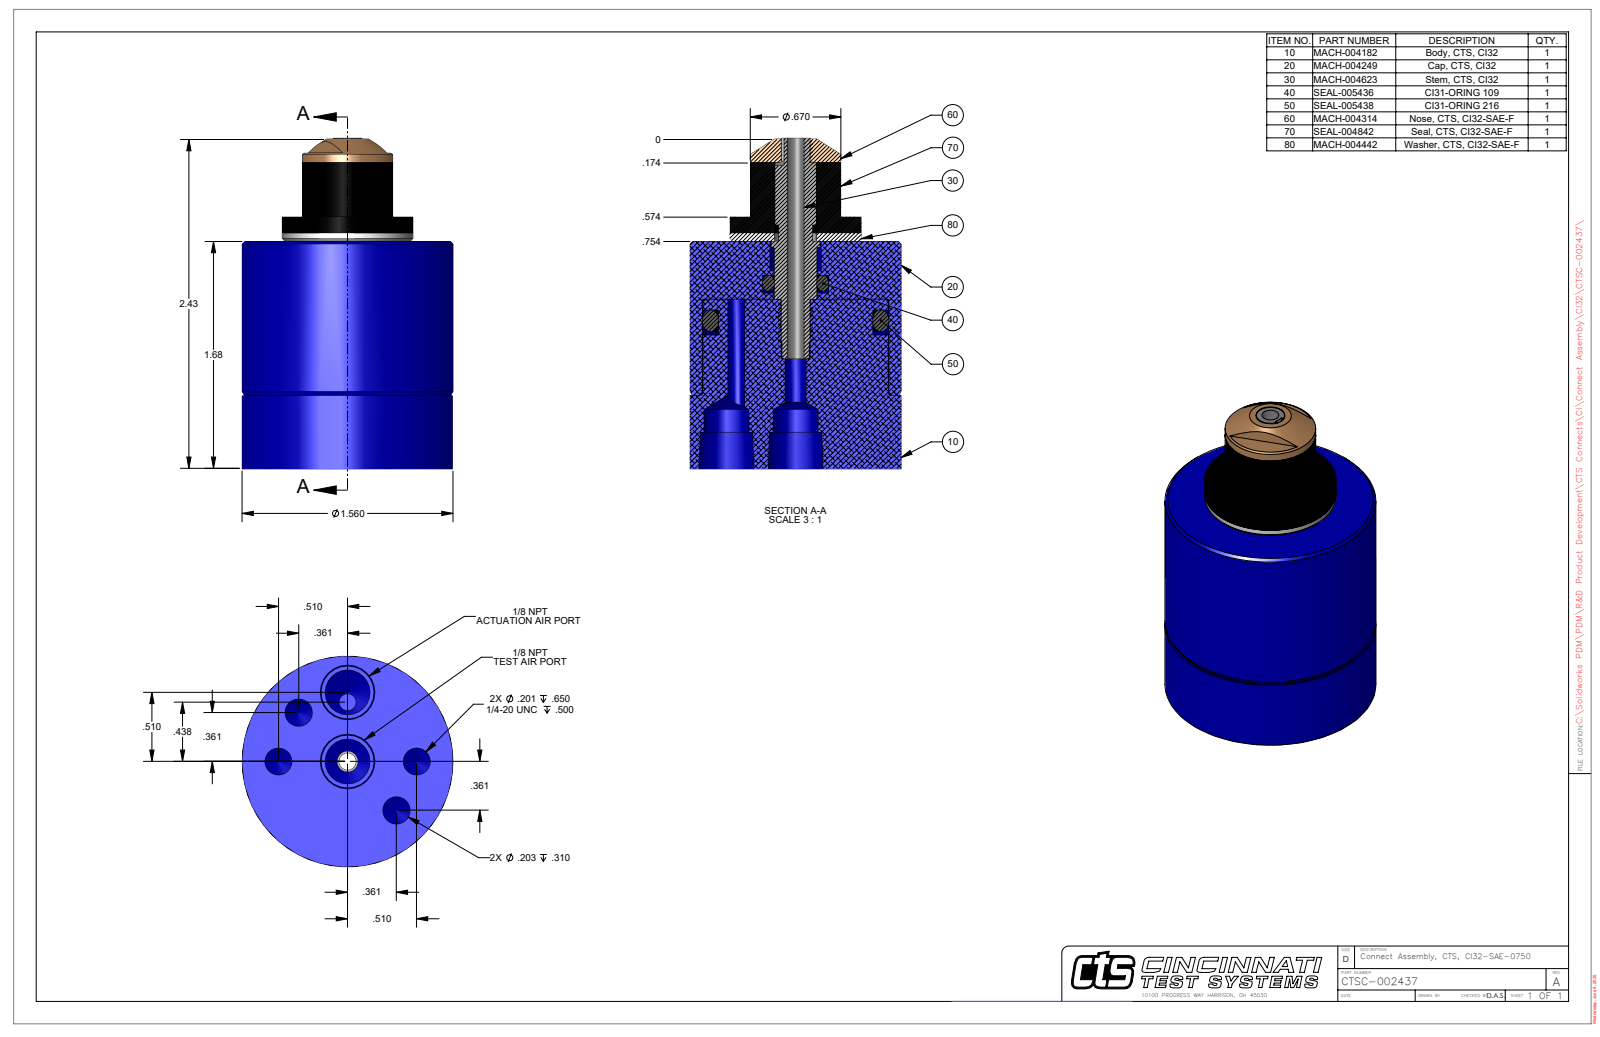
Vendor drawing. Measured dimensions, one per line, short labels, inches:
name: CTSC-002437
written by: SolidWorks 2023 (AUTOMOTIVE_DESIGN)
unit: in
bodies: 1 solid, 102 faces (29 planar, 39 cylindrical, 34 other)
size: 2.437 × 1.56 × 1.56
volume: 3.313 in³; area: 19.57 in²
holes: 2× ⌀0.125, 2× ⌀0.201, 2× ⌀0.203, 2× ⌀0.332, 1× ⌀0.156, 1× ⌀0.314, 1× ⌀0.38, 1× ⌀1.377
bosses: 1× ⌀1.56, 1× ⌀1.365, 1× ⌀0.97, 1× ⌀0.67, 1× ⌀0.357, 1× ⌀0.31
rounds: 1× R0.106
face distances: 1.677, 1.857, 0.18, 0.542, 1.135, 1.315, 2.327, 1.785, 0.65, 0.47
hole spacings: 0.51, 0.39, 0.942, 0.672, 0.721, 0.072, 0.369, 0.437
